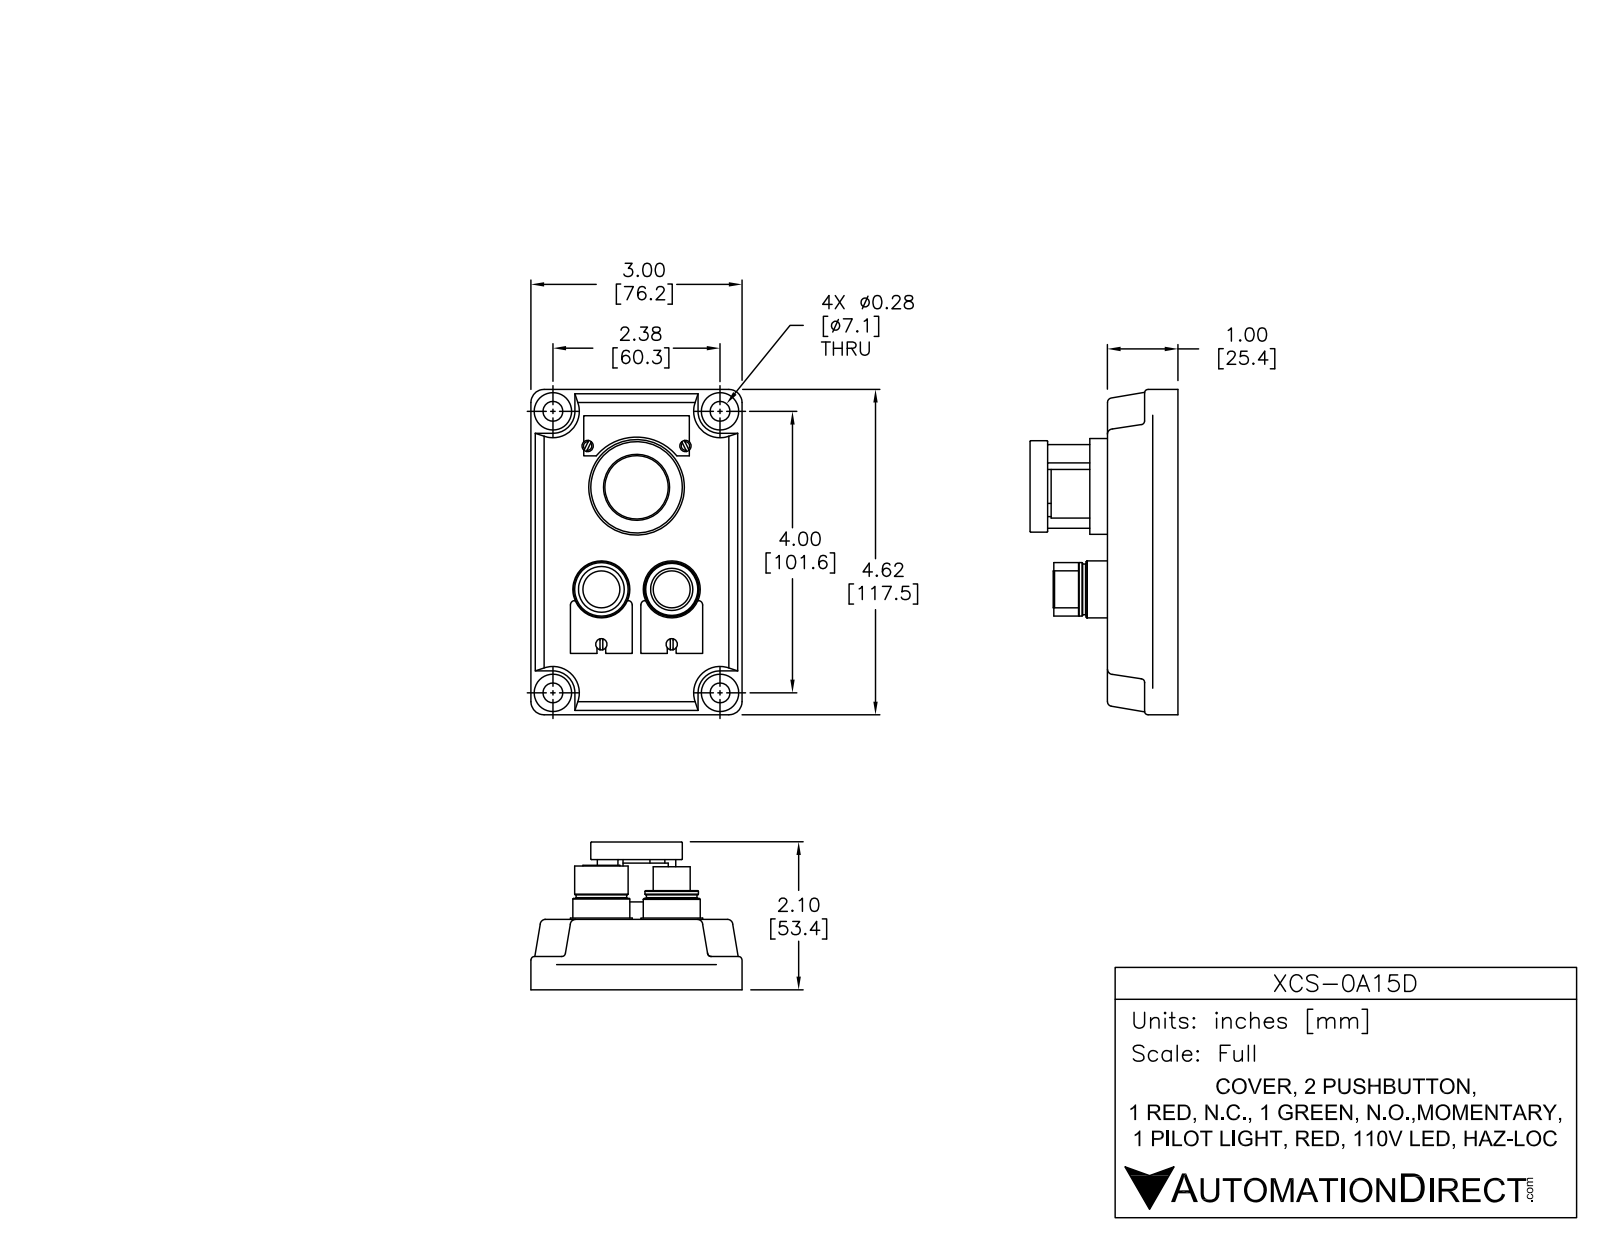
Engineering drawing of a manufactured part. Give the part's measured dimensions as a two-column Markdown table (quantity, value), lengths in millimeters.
| quantity | value |
| --- | --- |
| part name | XCS-0A15D |
| STEP written by | SolidWorks 2015 (AUTOMOTIVE_DESIGN) |
| units | millimeters |
| bodies | 39 solids, 853 faces (412 planar, 268 cylindrical, 173 other) |
| overall size | 117.47 × 98.23 × 79.05 |
| volume | 201 368 mm³ |
| surface area | 90 187 mm² |
| round holes (diameter × count) | 3 × 4, 5.65 × 4, 7.24 × 4, 18 × 2, 6.3 × 1, 16.1 × 1, 17.25 × 1, 17.5 × 1, 22.61 × 1, 32 × 1 |
| round bosses / shafts (diameter × count) | 4.06 × 8, 11.6 × 4, 6.35 × 4, 6 × 4, 20 × 2, 19.8 × 2, 18.2 × 2, 13.25 × 2 |
| partial cylindrical surfaces (radius × count) | 1 × 18, 2 × 16, 1.5 × 12, 0.76 × 8, 3 × 8, 6.35 × 8, 1.4 × 6, 1.52 × 6 |
| main face-to-face distances | 26, 14.5, 0.82, 11.5, 25.5, 26.85, 49.35, 12.66, 13.34, 12.11 |
| hole center spacings | 8.5, 20.1, 22.27, 31.25, 32.39, 34.89, 40.24, 41.53 |
